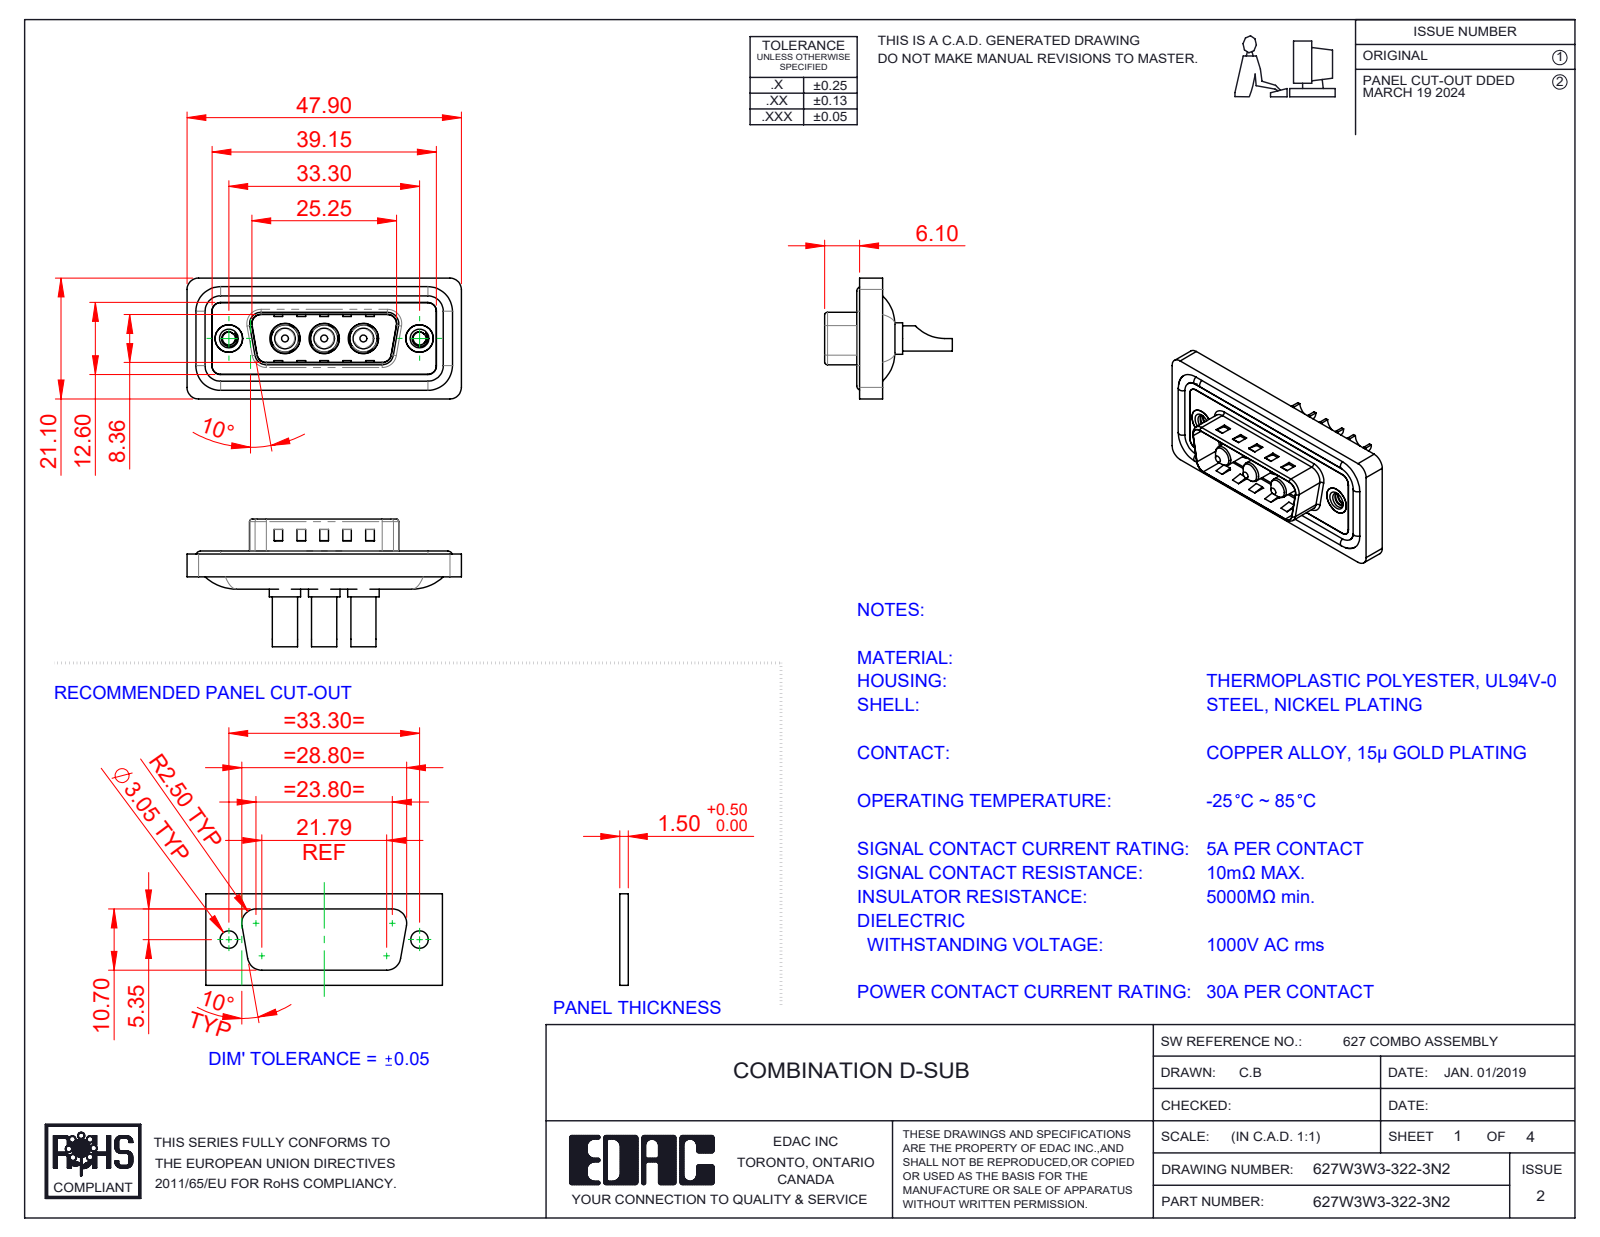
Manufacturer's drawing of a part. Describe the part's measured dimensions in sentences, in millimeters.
The part is named "627Combo Shell Front_15 Contacts; Power Pin_30A SC; 627W3W3-322-3N2; 627Combo Housing_3W3 (+3 more)". Its 3-D file was written by "SolidWorks 2023 (CONFIG_CONTROL_DESIGN)". It is 13 solids with 582 faces: 216 planar, 250 cylindrical and 116 other. Overall it measures 47.9 by 22.3 by 21.1 millimeters. Its volume is 5 658 cubic millimeters and its surface area 9 076 square millimeters. Round holes: 3 of diameter 3.5, 3 of diameter 4.85, 3 of diameter 5.3, 2 of diameter 2.26, 2 of diameter 4, 2 of diameter 4.8, 2 of diameter 5. Round bosses or shafts: 4 of diameter 1.6, 3 of diameter 5.5, 3 of diameter 5.2, 3 of diameter 4.75, 3 of diameter 4.4, 3 of diameter 3.75, 3 of diameter 3.6, 2 of diameter 4.9. Partial cylindrical surfaces (rounded edges, fillets, slot ends): 26 of radius 1.5, 20 of radius 2, 8 of radius 0.5, 8 of radius 1.6, 4 of radius 0.25, 4 of radius 0.6, 4 of radius 0.65, 4 of radius 0.9. The main face-to-face distances are 0.4, 1.1, 0.5, 1.6, 1.5, 3.1, 2.9, 0.82, 9.58, 2.5. The hole center spacings are 6.85, 9.8, 16.65, 23.5, 13.7, 33.3.
